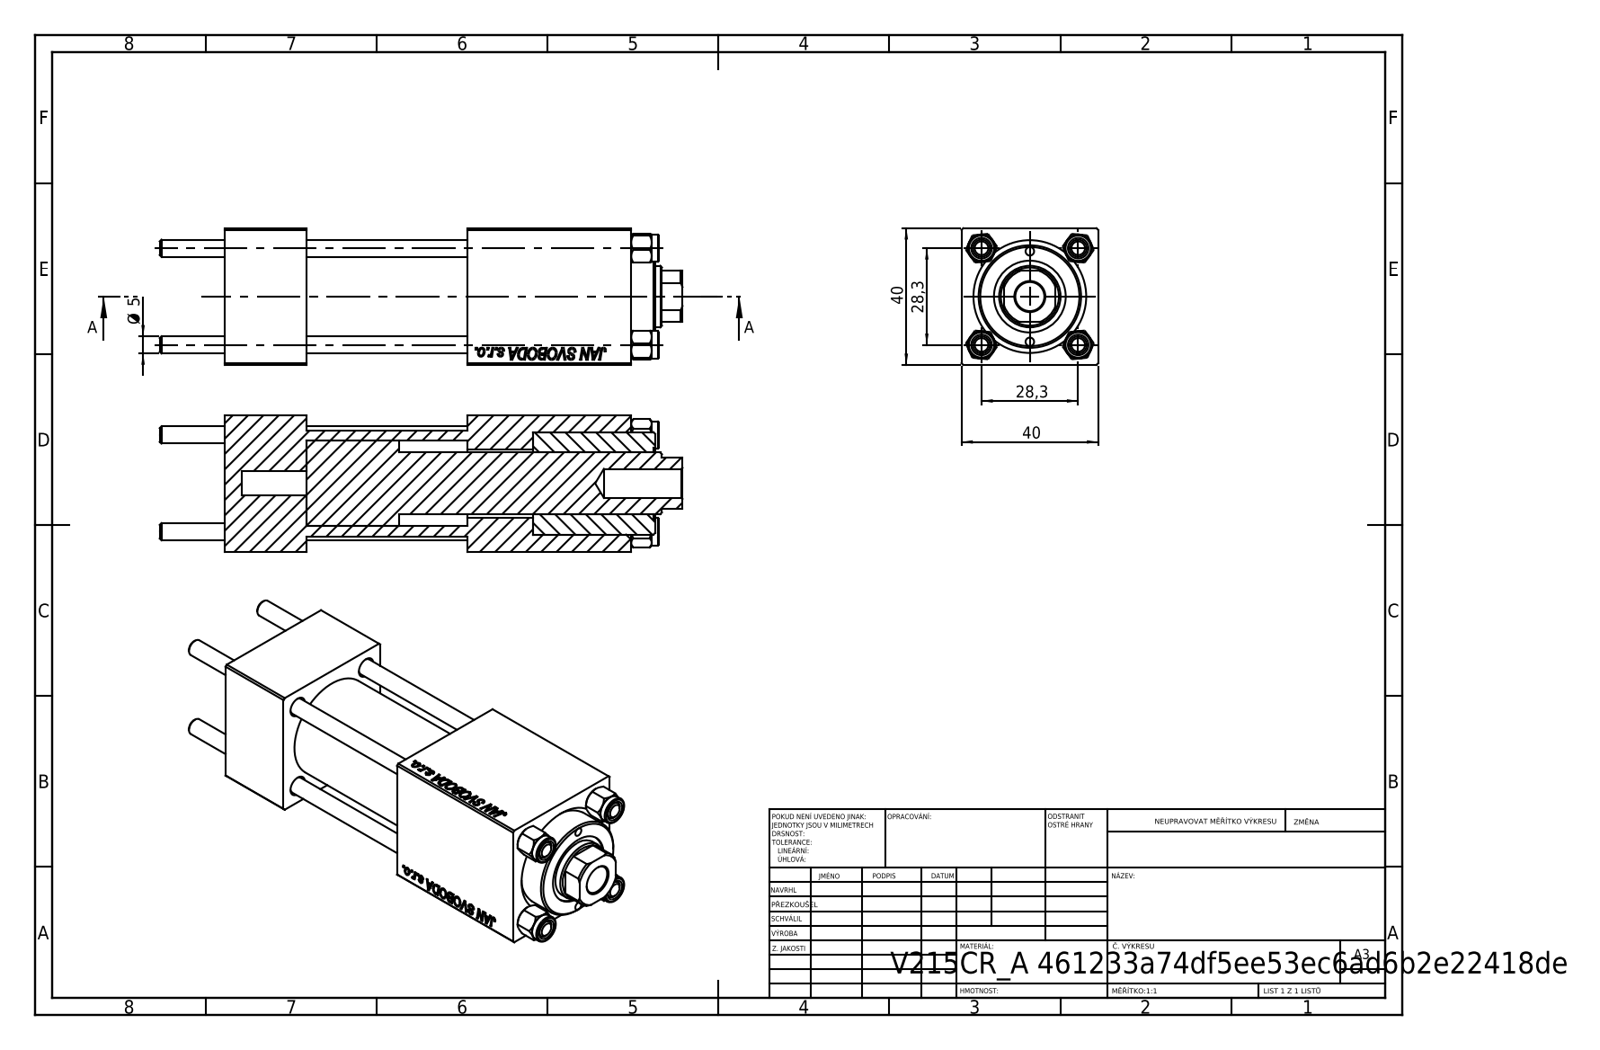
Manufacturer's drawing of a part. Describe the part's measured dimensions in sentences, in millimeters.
The part is named "NUT_M5; CR025_012_A_0_G_A_G_M_020_+#_##_TYCINKA; V215_VC_A; V215CR_VCP (+1 more)". Its 3-D file was written by "SolidWorks 2019 (CONFIG_CONTROL_DESIGN)". It is 11 solids with 1134 faces: 518 planar, 80 cylindrical and 536 other. Overall it measures 153 by 40 by 40 millimeters. Its volume is 152 313 cubic millimeters and its surface area 61 335 square millimeters. Round holes: 4 of diameter 5, 3 of diameter 20, 2 of diameter 2.5, 2 of diameter 7, 2 of diameter 13.16, 1 of diameter 8.5, 1 of diameter 18, 1 of diameter 21, 1 of diameter 25, 1 of diameter 30. Round bosses or shafts: 4 of diameter 8, 1 of diameter 31. Partial cylindrical surfaces (rounded edges, fillets, slot ends): 1 of radius 8.5. The main face-to-face distances are 40, 24, 71, 47, 90.3, 66.3, 19.3, 119, 95, 48. The hole center spacings are 14.18, 20.01, 28.3, 30.84, 13.25, 40.02, 26.5, 72.
